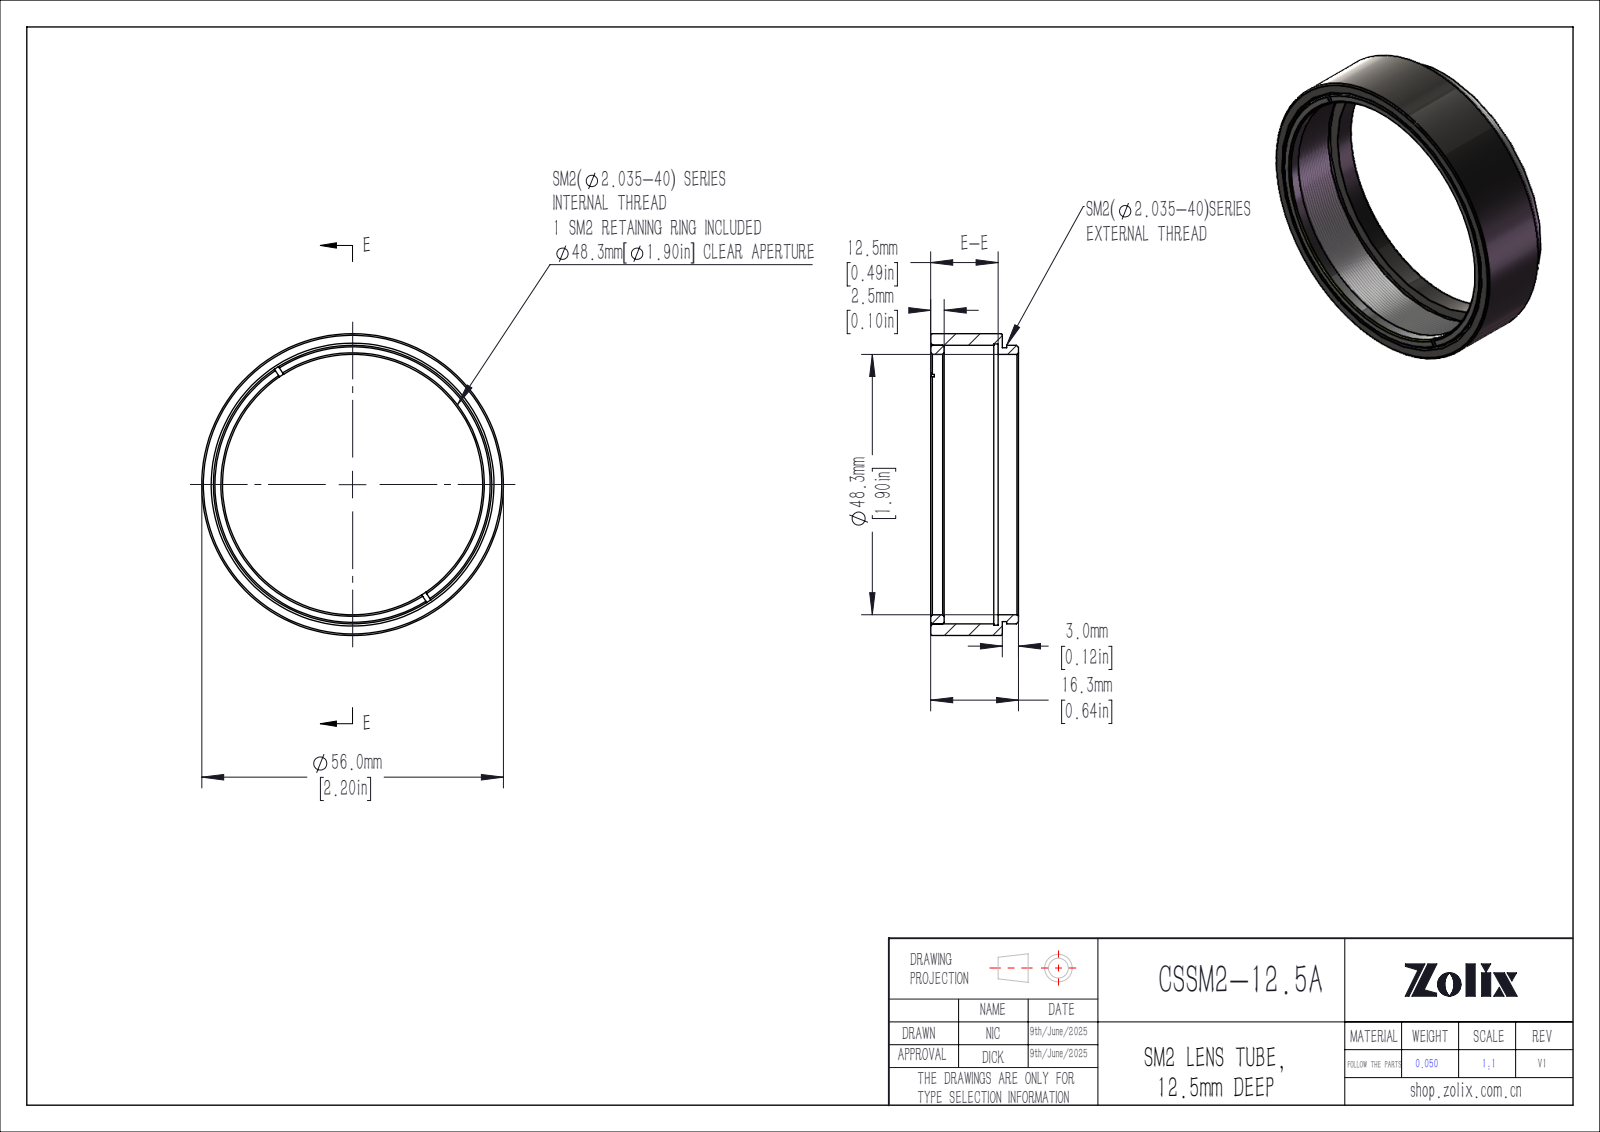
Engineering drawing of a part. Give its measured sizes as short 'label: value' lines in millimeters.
name: CSSM2-12.5A
written by: SolidWorks 2020 (CONFIG_CONTROL_DESIGN)
unit: mm
bodies: 2 solids, 378 faces (63 planar, 38 cylindrical, 277 other)
size: 56 × 56 × 16.3
volume: 6 370 mm³; area: 7 992 mm²
holes: 1× ⌀48.3, 1× ⌀52.2
bosses: 1× ⌀56, 1× ⌀51.69, 1× ⌀50.8
rounds: 1× R27.98
face distances: 0.8, 13.3, 12.5, 10, 2.5, 10.8, 3, 16.3, 13.8, 3.8
